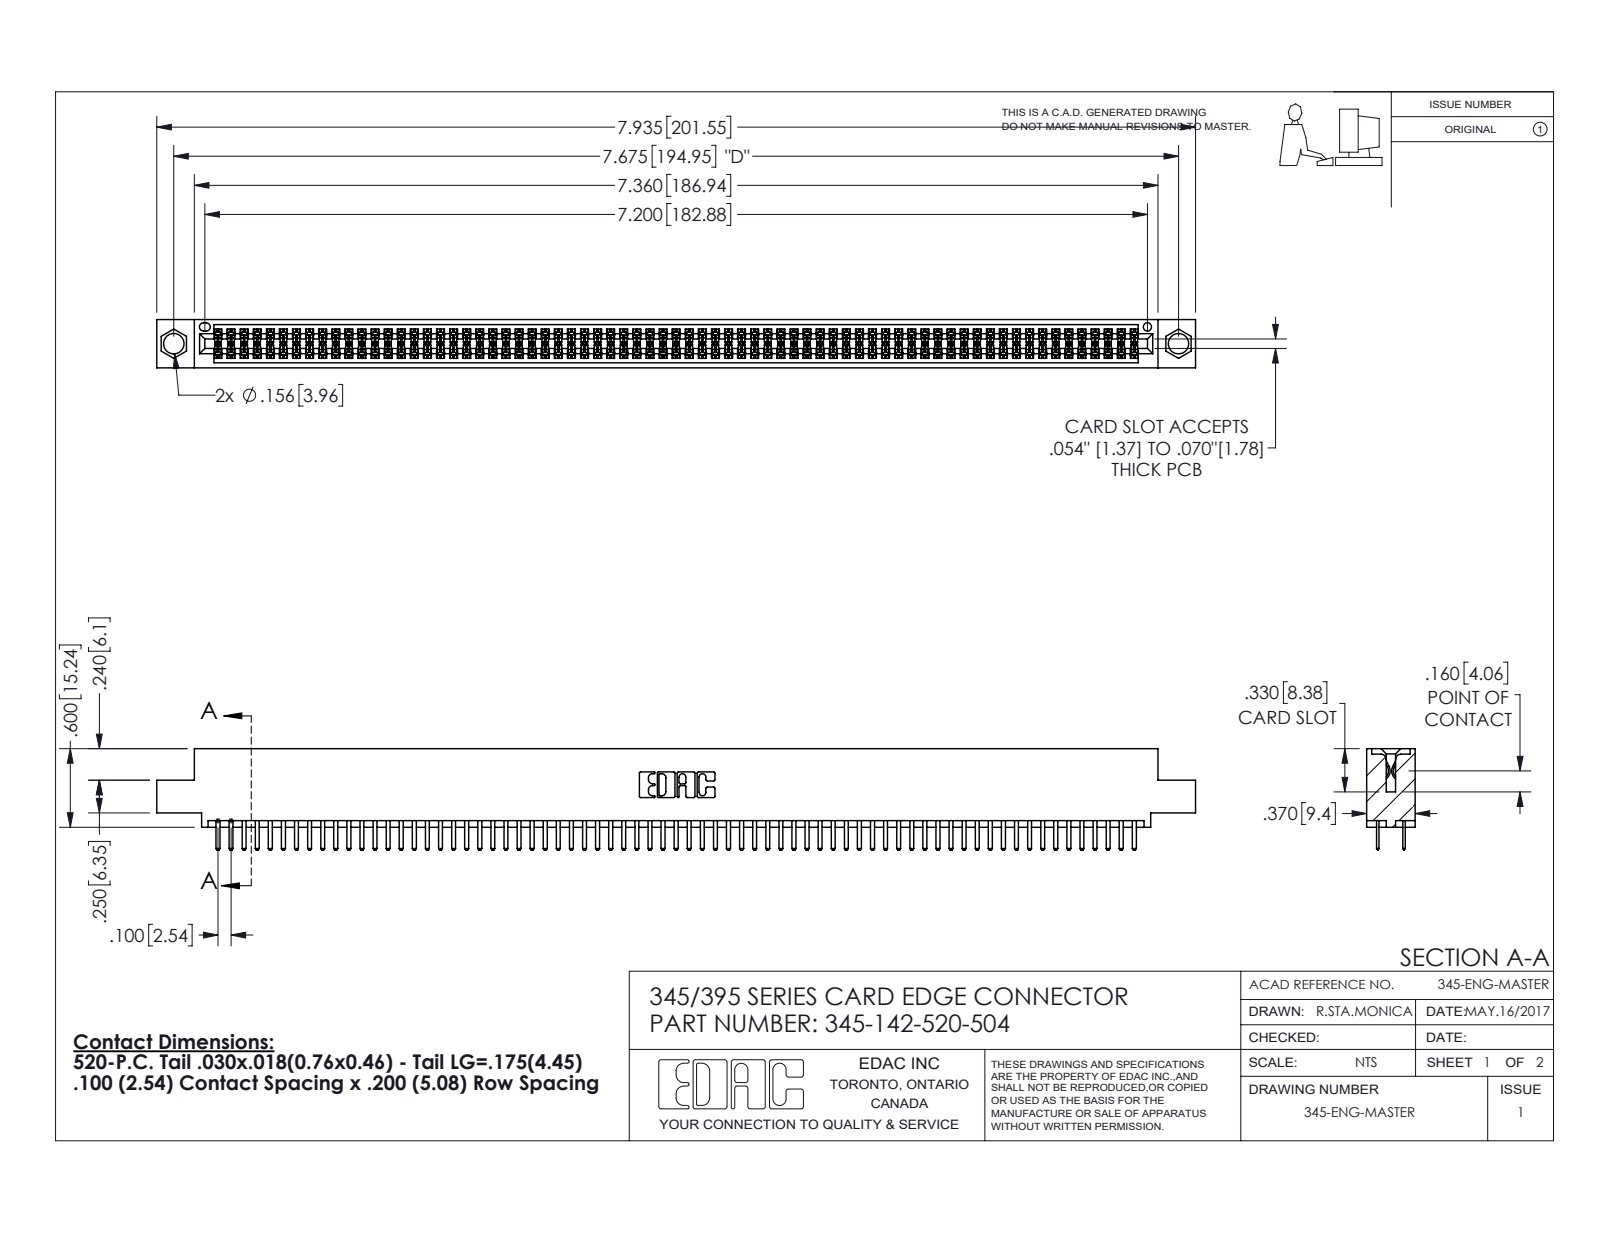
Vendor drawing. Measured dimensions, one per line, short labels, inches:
name: 345-292-001_345-293-120; 345 Part_0.110 Offset - 0.156 Dia-TI; 345-142-520-504
written by: SolidWorks 2020 (CONFIG_CONTROL_DESIGN)
unit: in
bodies: 143 solids, 7812 faces (5068 planar, 2744 cylindrical, 0 other)
size: 7.935 × 0.775 × 0.37
volume: 1.196 in³; area: 45.5 in²
holes: 2× ⌀0.156, 1× ⌀0.064
rounds: 213× R0.006, 146× R0.01, 22× R0.01, 6× R0.007, 6× R0.031, 3× R0.026, 2× R0.014, 2× R0.019
face distances: 0.298, 0.072, 0.2, 0.37, 0.098, 0.272, 0.025, 0.225, 0.022, 0.072
hole spacings: 0.27, 7.439, 7.675
